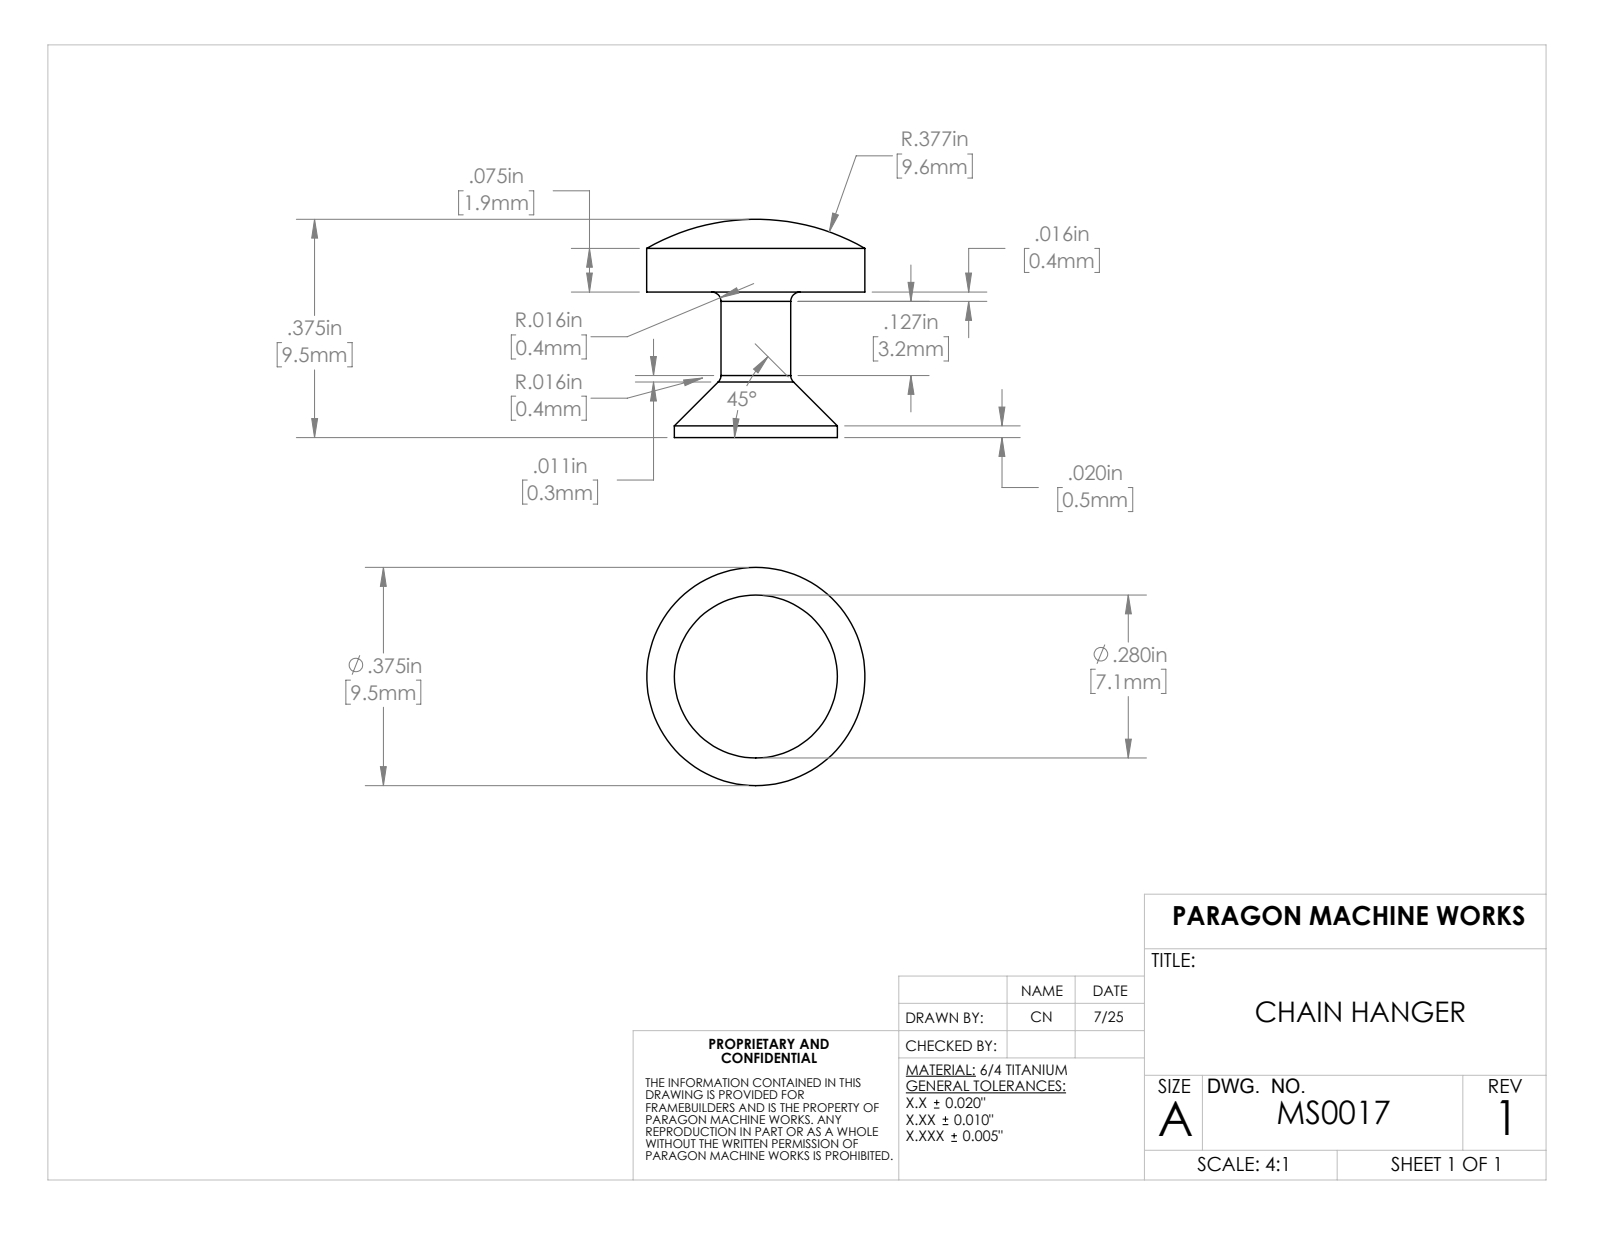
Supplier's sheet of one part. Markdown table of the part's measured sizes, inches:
| quantity | value |
| --- | --- |
| part name | MS0017 |
| STEP written by | SolidWorks 2023 (AUTOMOTIVE_DESIGN) |
| units | inches |
| bodies | 1 solid, 16 faces (2 planar, 6 cylindrical, 8 other) |
| overall size | 0.375 × 0.375 × 0.375 |
| volume | 0.017 in³ |
| surface area | 0.51 in² |
| round bosses / shafts (diameter × count) | 0.375 × 1, 0.28 × 1, 0.12 × 1 |
| main face-to-face distances | 0.25 |
